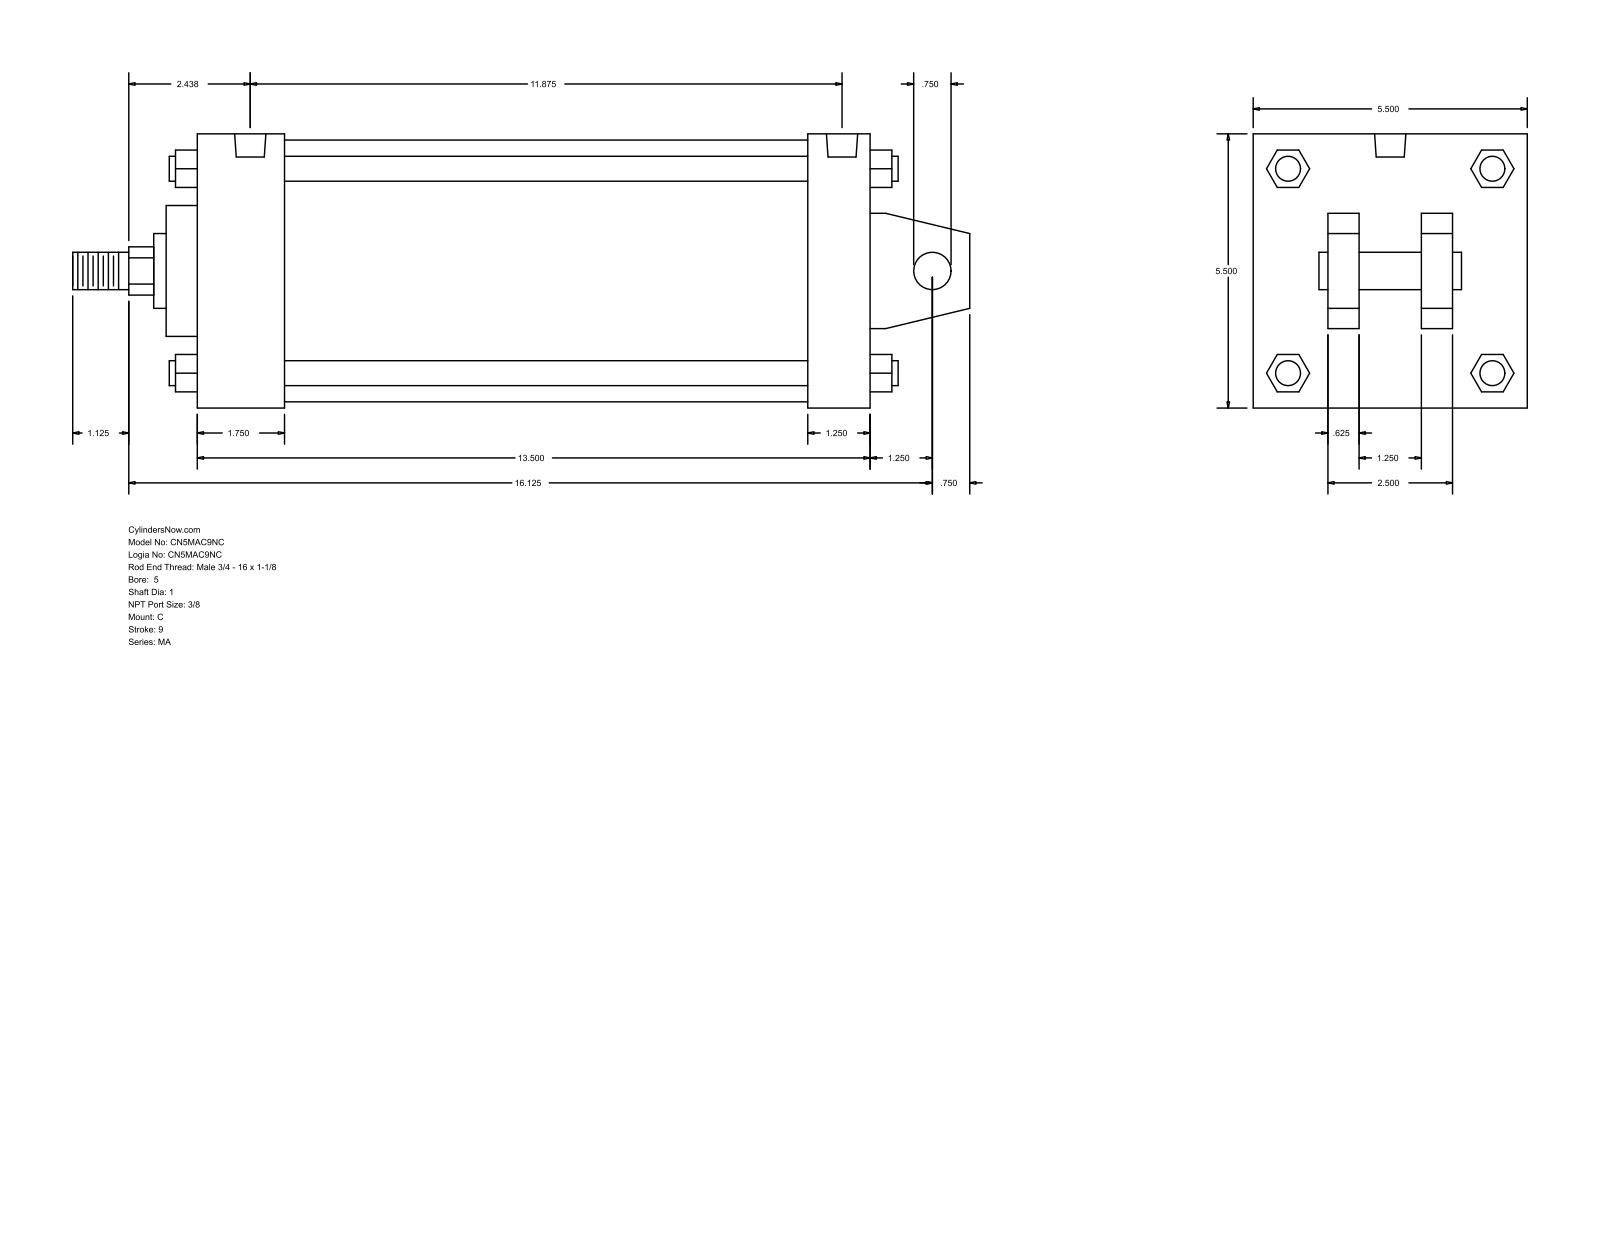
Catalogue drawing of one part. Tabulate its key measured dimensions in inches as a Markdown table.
| quantity | value |
| --- | --- |
| part name | MA_C__0500_1 |
| STEP written by | GSSL Pune (CONFIG_CONTROL_DESIGN) |
| units | inches |
| bodies | 0 solids, 141 faces (109 planar, 32 cylindrical, 0 other) |
| overall size | 18 × 5.5 × 5.5 |
| round holes (diameter × count) | 0.437 × 4, 0.627 × 2 |
| round bosses / shafts (diameter × count) | 0.5 × 4, 0.75 × 2, 5.25 × 1, 2.625 × 1, 1.5 × 1, 1 × 1 |
| partial cylindrical surfaces (radius × count) | 0.484 × 1 |
| main face-to-face distances | 5.5, 13.5, 0.625, 12.25, 1.25, 1.75, 10.5, 11.75, 1.5, 4 |
| hole center spacings | 11.5, 0.187, 0.188, 11.687, 11.688, 11.875 |
